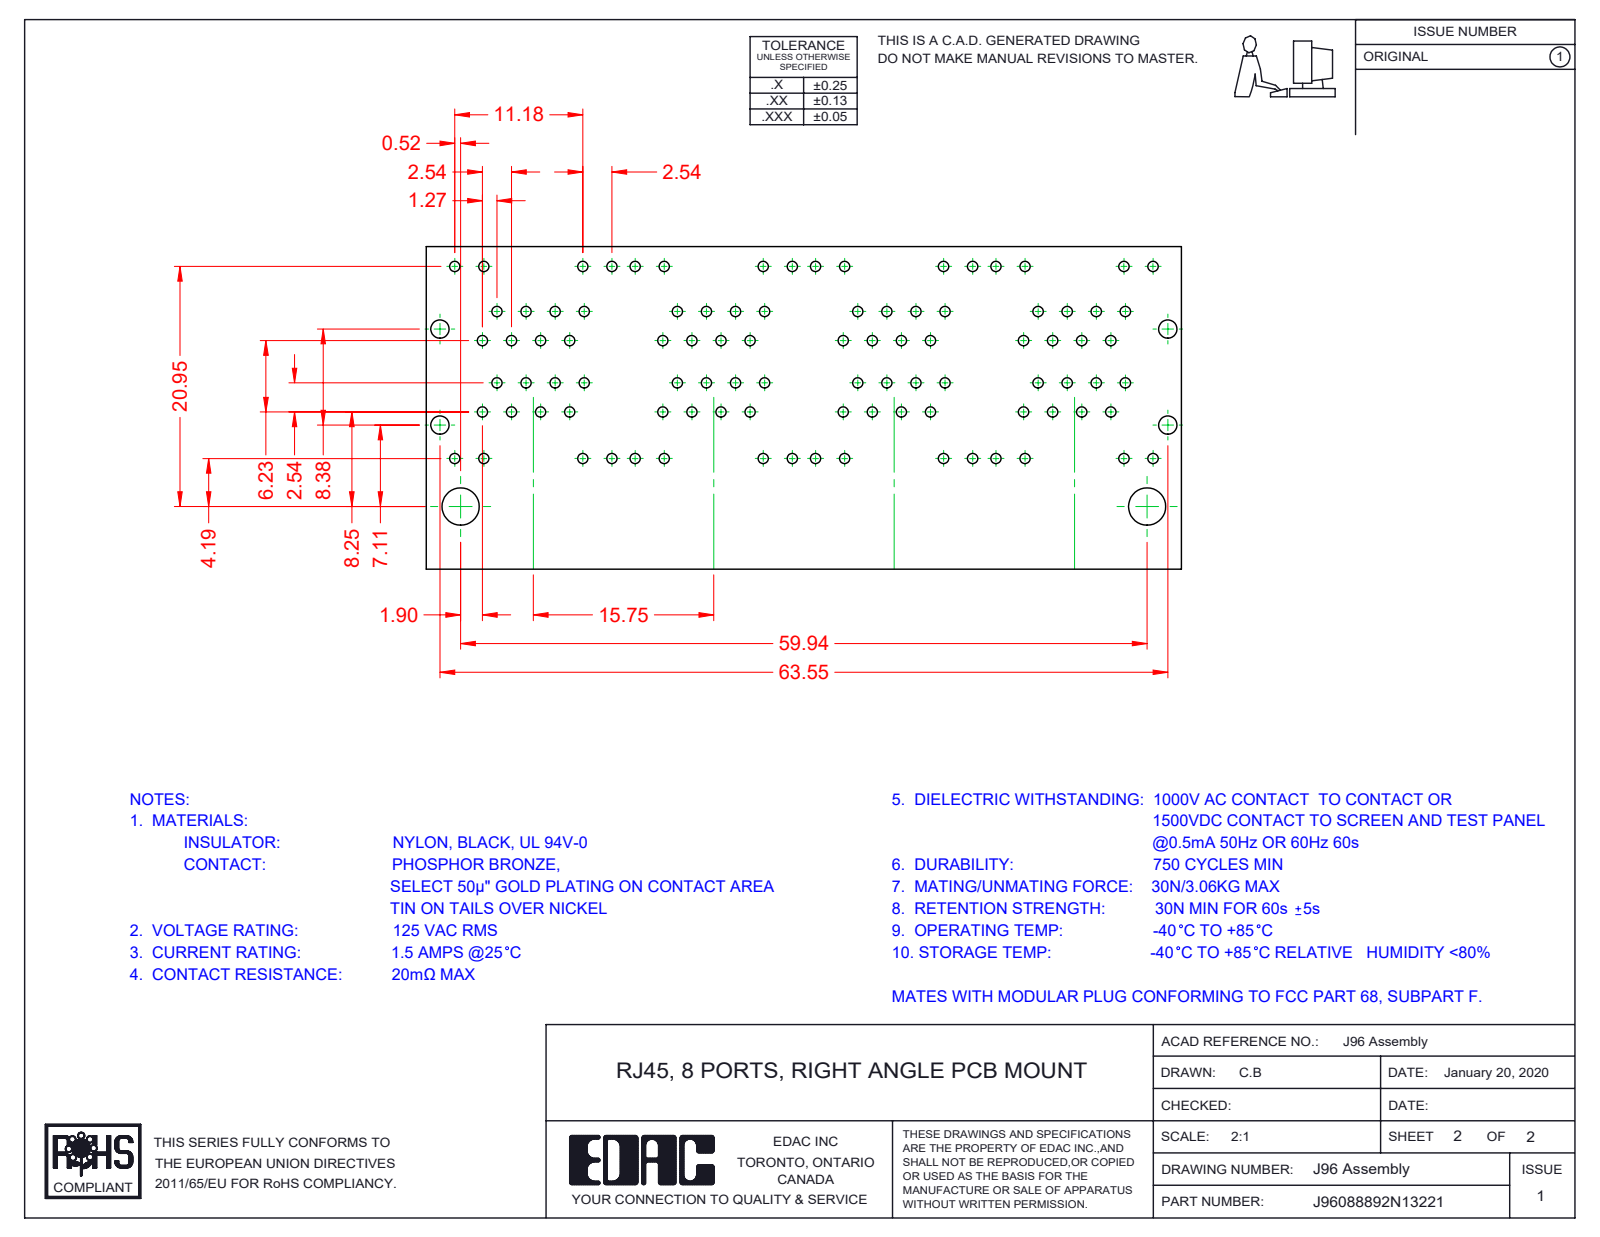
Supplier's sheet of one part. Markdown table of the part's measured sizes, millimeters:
| quantity | value |
| --- | --- |
| part name | J96088892N13221; 96 Back Plate_8 Ports; 96 Shield_8 Ports LED - EMI; 96 Grounding_8 Ports (+8 more) |
| STEP written by | SolidWorks 2016 (CONFIG_CONTROL_DESIGN) |
| units | millimeters |
| bodies | 96 solids, 7804 faces (6105 planar, 1388 cylindrical, 311 other) |
| overall size | 67.35 × 31.38 × 28.68 |
| volume | 24 149 mm³ |
| surface area | 63 596 mm² |
| round holes (diameter × count) | 1.7 × 3 |
| round bosses / shafts (diameter × count) | 1.68 × 3 |
| partial cylindrical surfaces (radius × count) | 0.25 × 124, 0.35 × 73, 1 × 72, 0.5 × 49, 0.91 × 32, 0.2 × 27, 0.27 × 14, 0.7 × 11 |
| main face-to-face distances | 15.75, 0.35, 9.95, 1.17, 1.6, 0.54, 9.98, 10.18, 12.67, 3.37 |
| hole center spacings | 15.75, 31.5 |
